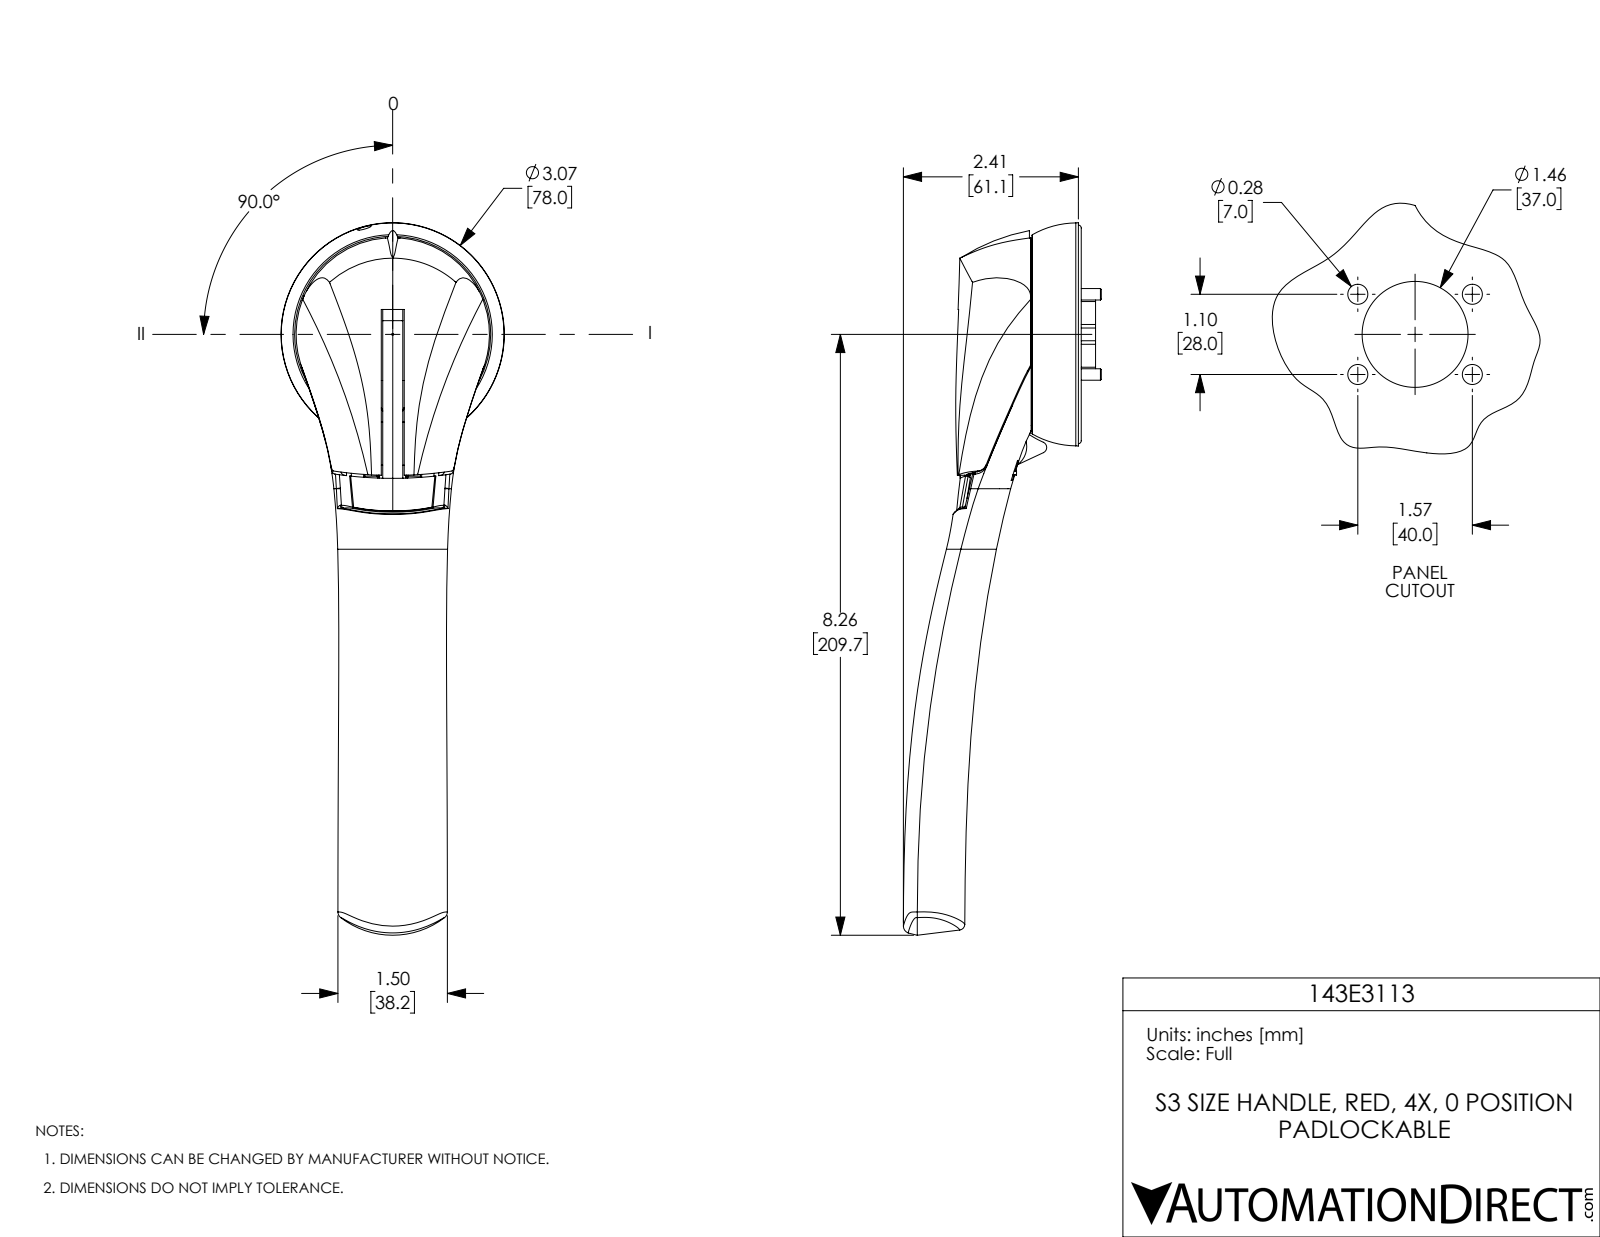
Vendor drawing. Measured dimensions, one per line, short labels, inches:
name: 143E3113
written by: SolidWorks 2017 (AUTOMOTIVE_DESIGN)
unit: in
bodies: 8 solids, 1514 faces (806 planar, 544 cylindrical, 164 other)
size: 9.793 × 3.07 × 2.721
volume: 12.91 in³; area: 100.4 in²
holes: 6× ⌀0.157, 4× ⌀0.339, 4× ⌀0.425, 3× ⌀0.03, 2× ⌀0.169, 2× ⌀0.362, 1× ⌀0.118, 1× ⌀0.189, 1× ⌀2.992
bosses: 11× ⌀0.02, 4× ⌀0.335, 4× ⌀0.315, 3× ⌀0.089, 3× ⌀0.069, 2× ⌀0.228, 1× ⌀2.819, 1× ⌀2.701
rounds: 221× R0.01, 20× R0.015, 20× R0.034, 15× R0.03, 4× R0.039, 3× R0.025, 3× R5.437, 2× R0.079
face distances: 0.024, 0.701, 0.713, 0.689, 0.035, 0.276, 0.102, 0.173, 0.244, 0.047
hole spacings: 0.961, 0.309, 0.669, 1.098, 1.102, 1.203, 1.575, 1.881
